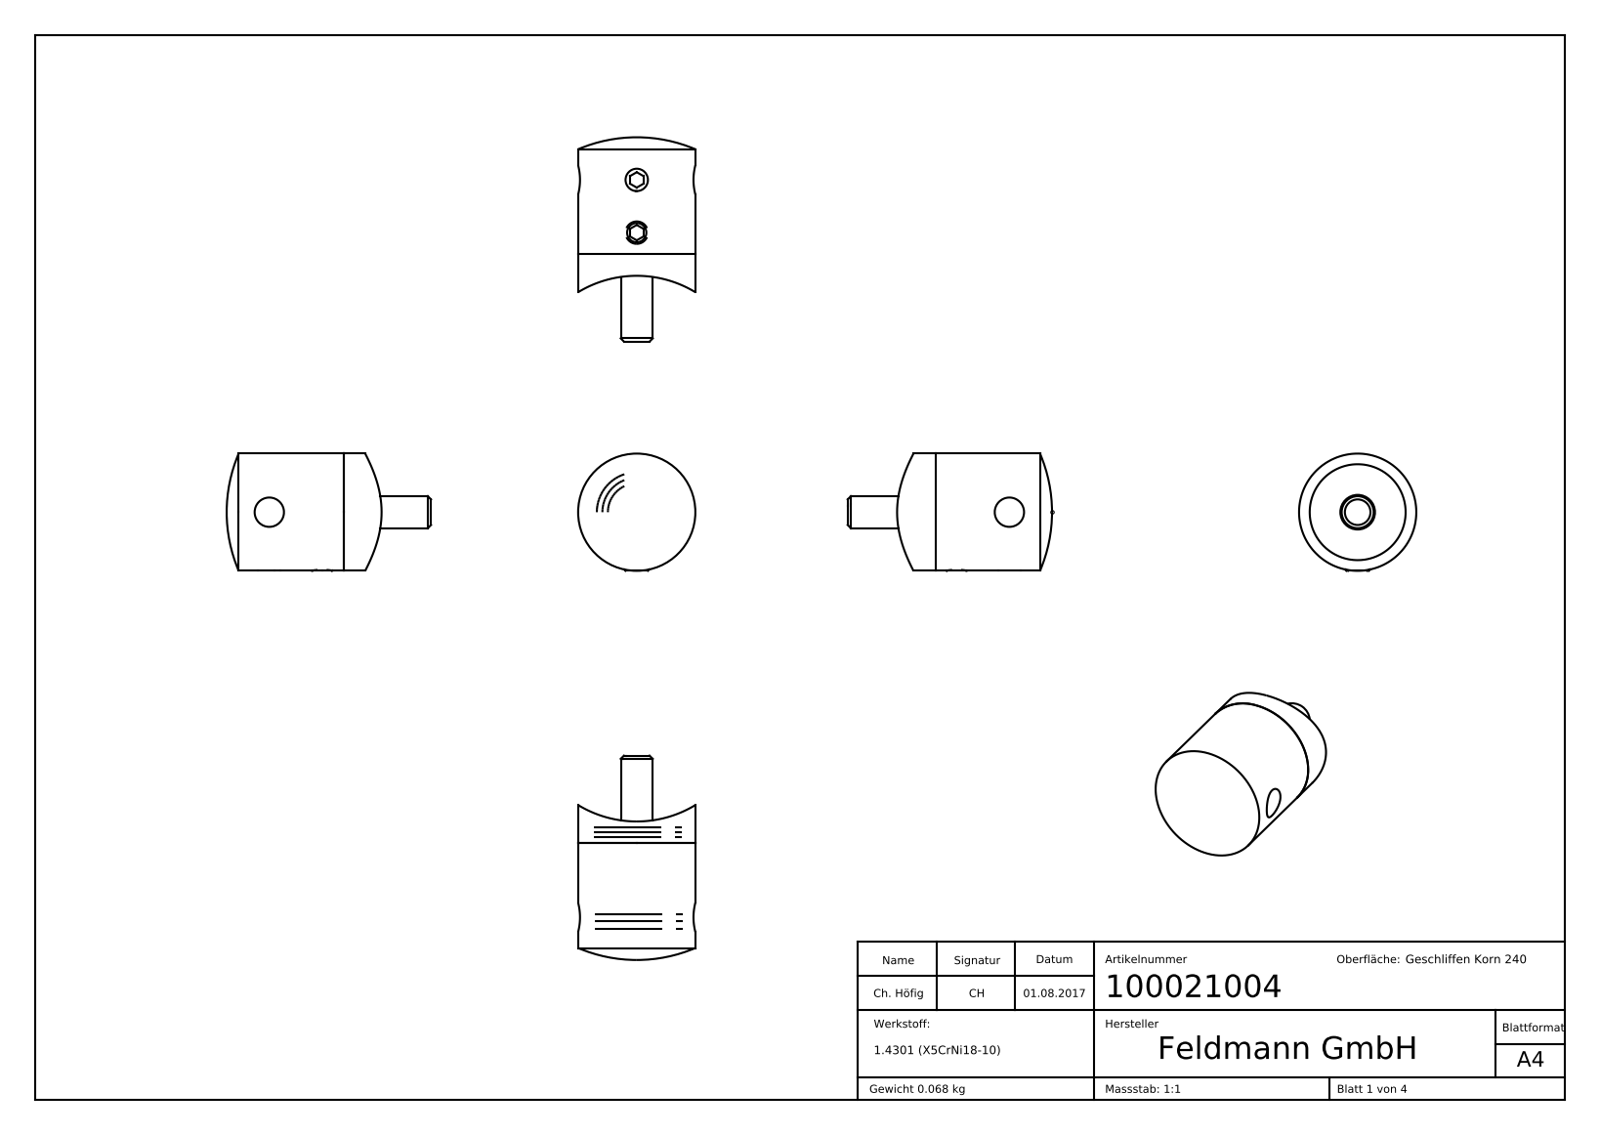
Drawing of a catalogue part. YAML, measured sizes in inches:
part_name: "DIN 914 M5x5_DIN914 M5x5; DIN7991 M6x25; DIN913 M5x8_DIN913 M5x8; DIN913 M5x8 (+7 more)"
step_written_by: "SolidWorks 2018 (CONFIG_CONTROL_DESIGN)"
units: inches
bodies: {solids: 5, faces: 64, planar: 36, cylindrical: 14, other: 14}
overall_size: [3.228, 1.319, 0.866]
volume: 0.539
surface_area: 9.173
round_holes:
  - {diameter: 0.165, count: 2}
  - {diameter: 0.256, count: 1}
  - {diameter: 0.402, count: 1}
  - {diameter: 0.476, count: 1}
  - {diameter: 0.709, count: 1}
round_bosses_or_shafts:
  - {diameter: 0.197, count: 2}
  - {diameter: 0.866, count: 1}
  - {diameter: 0.472, count: 1}
  - {diameter: 0.236, count: 1}
face_to_face_distances: [0.378, 0.299, 0.079, 0.217, 0.083, 0.161, 1.01, 0.793, 0.711, 0.632]
hole_center_spacings: [0.488]
